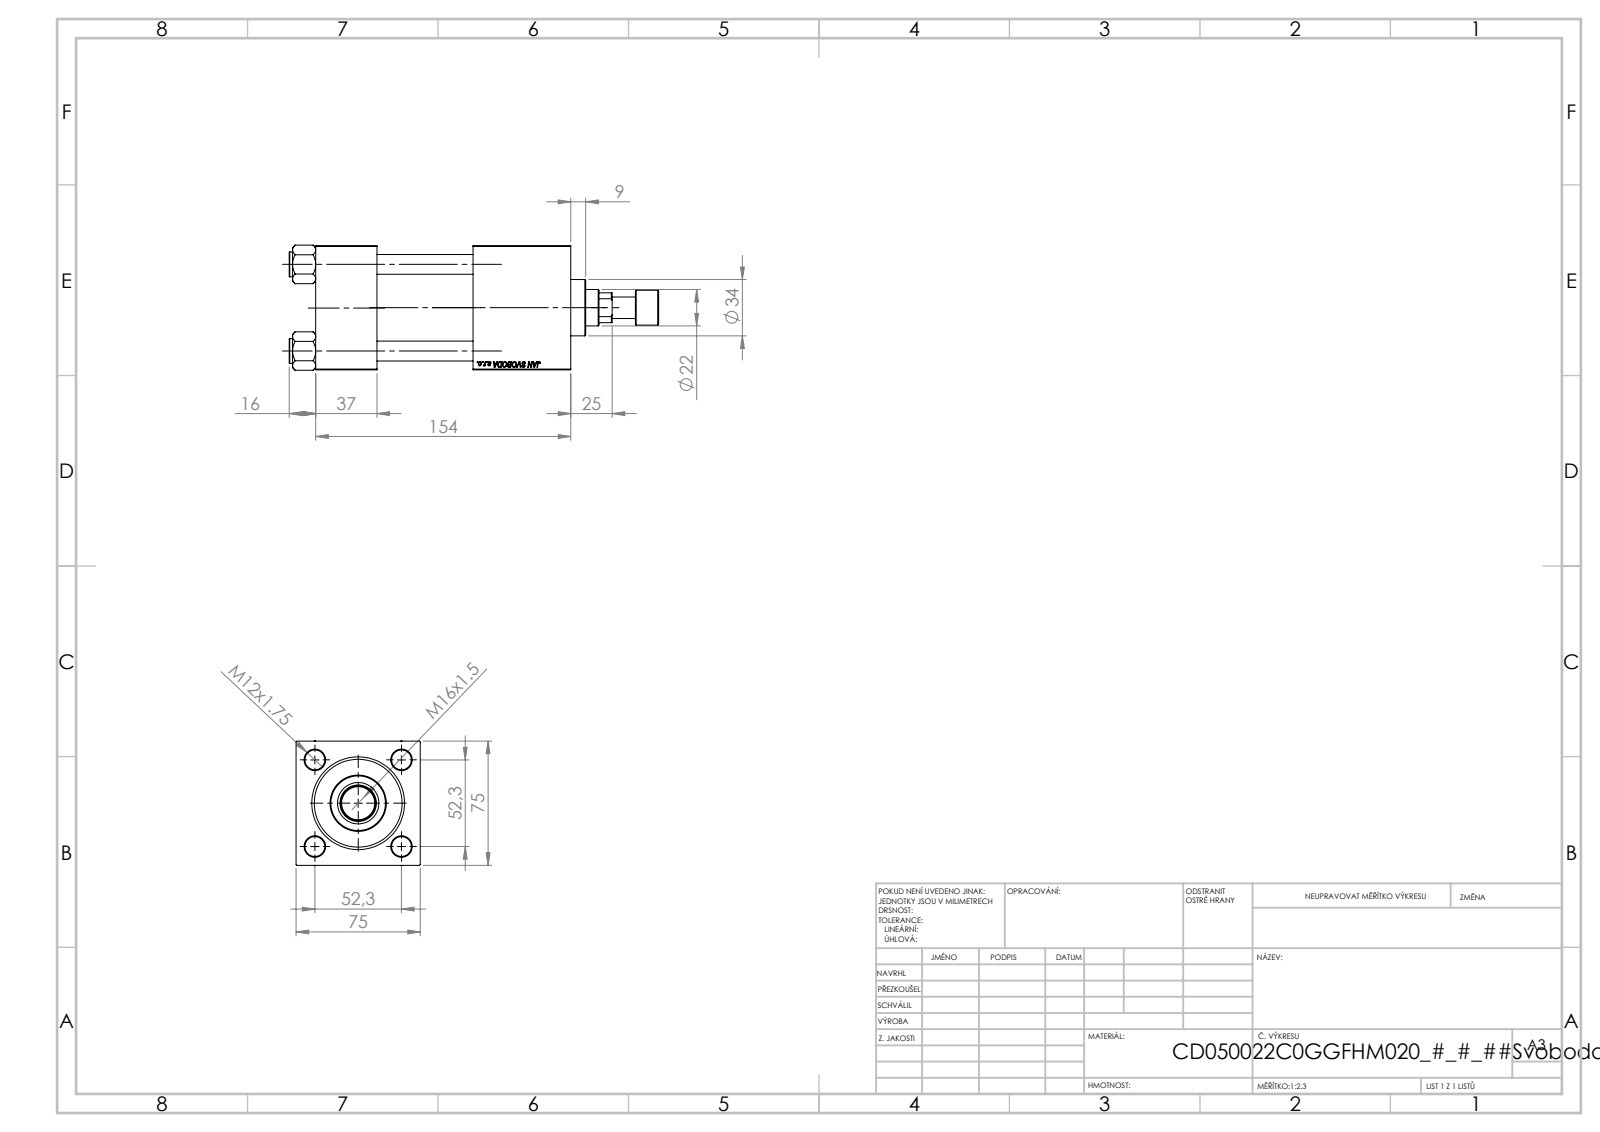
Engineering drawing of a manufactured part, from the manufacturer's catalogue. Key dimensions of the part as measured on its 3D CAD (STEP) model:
Part name (STEP PRODUCT): V215CD_VCP_C; NUT_M5_V215CD_C; V215CD_VC_C; V215CD_Body_C (+2 more)
STEP written by: SolidWorks 2019 (CONFIG_CONTROL_DESIGN)
Units: millimetres
Bodies: 12 solids, 1160 faces (529 planar, 91 cylindrical, 540 other)
Overall size (bounding box): 223 × 75.54 × 75
Volume: 663 542 mm³ · Surface area: 149 450 mm²
Round holes (diameter × count): ⌀12 ×4, ⌀7 ×2, ⌀20.96 ×2, ⌀30 ×2, ⌀10.5 ×1, ⌀22 ×1, ⌀25 ×1, ⌀41 ×1, ⌀50 ×1, ⌀53 ×1
Round bosses / shafts (diameter × count): ⌀15 ×4, ⌀56 ×1, ⌀34 ×1, ⌀21 ×1, ⌀13 ×1
Main face-to-face distances: 75, 37, 154, 117, 59, 95, 58, 125.3, 88.3, 30.3
Hole centre spacings: 36.98, 52.3, 73.96, 93.5
